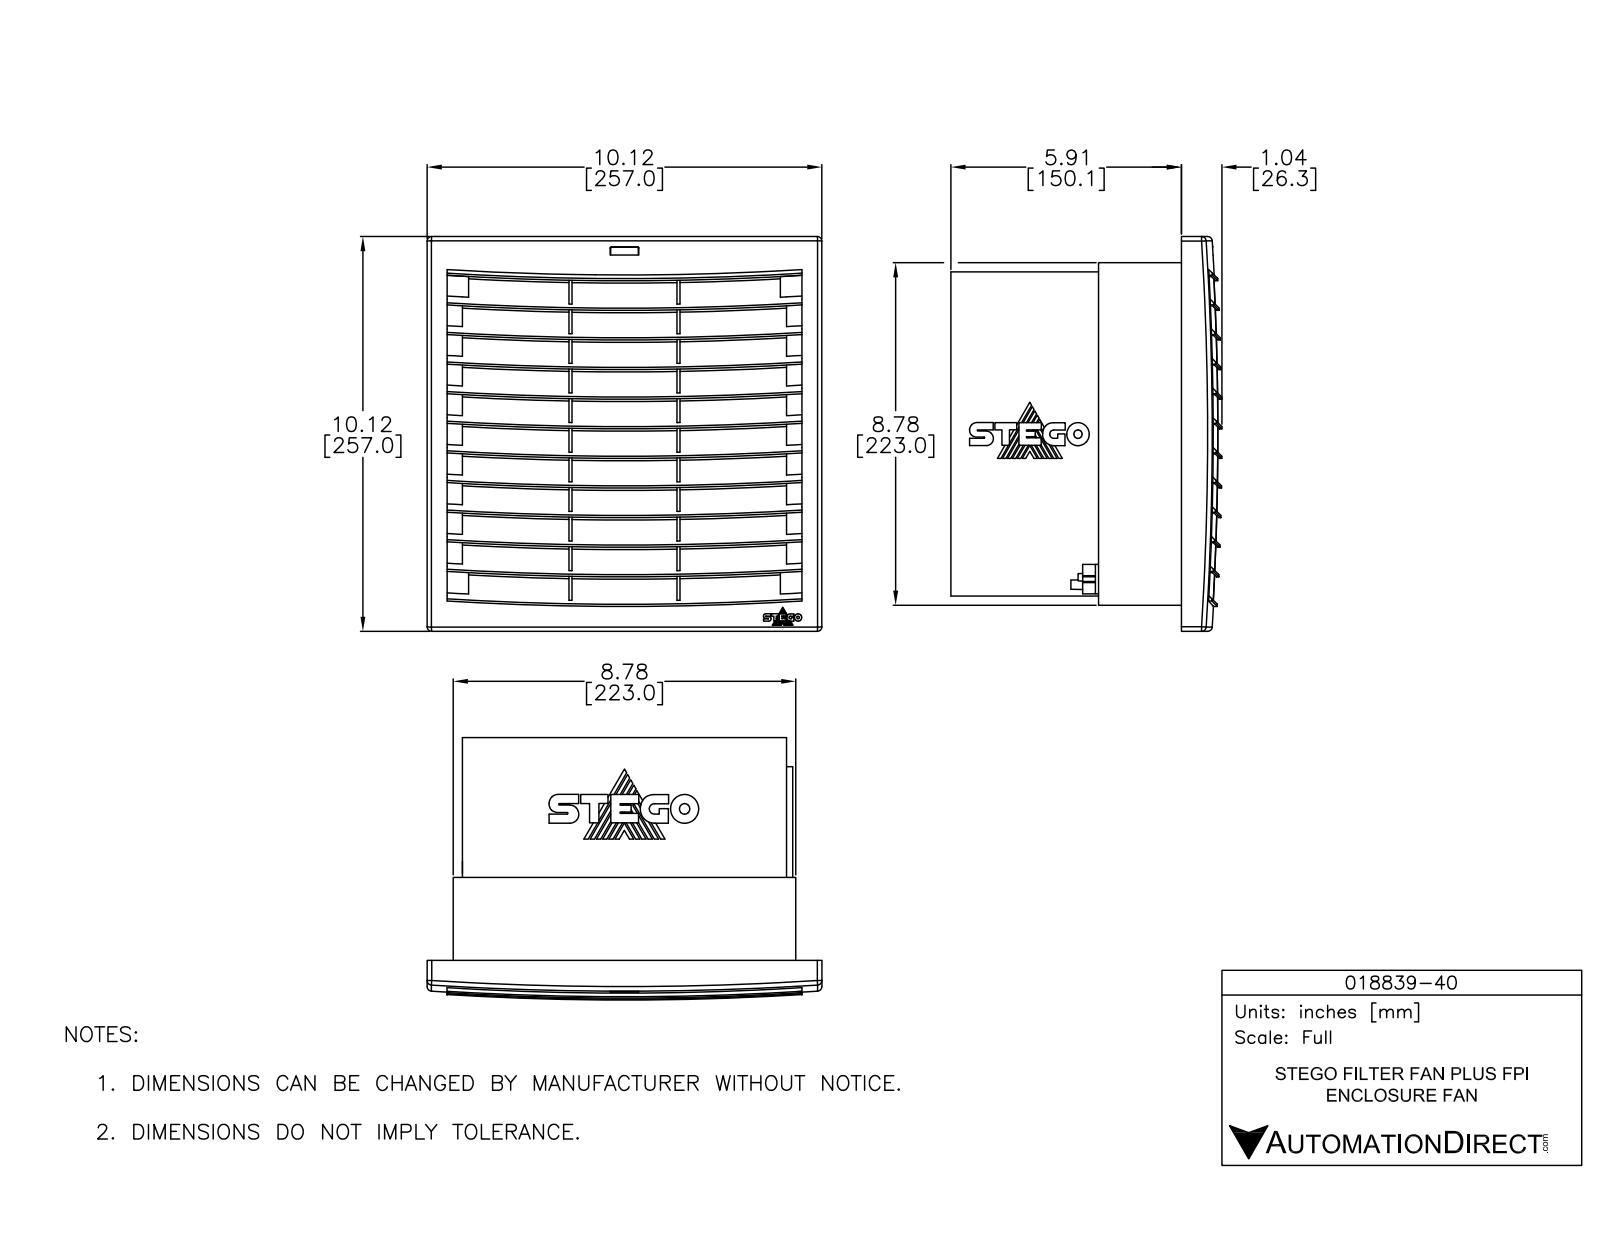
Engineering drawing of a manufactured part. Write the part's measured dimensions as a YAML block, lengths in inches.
part_name: "018839-40"
step_written_by: "SolidWorks 2018 (AUTOMOTIVE_DESIGN)"
units: inches
bodies: {solids: 1, faces: 808, planar: 462, cylindrical: 346, other: 0}
overall_size: [10.118, 10.118, 6.811]
volume: 155
surface_area: 918.5
round_holes:
  - {diameter: 2.268, count: 1}
  - {diameter: 3.018, count: 1}
  - {diameter: 3.769, count: 1}
  - {diameter: 4.487, count: 1}
  - {diameter: 4.52, count: 1}
  - {diameter: 5.27, count: 1}
  - {diameter: 5.42, count: 1}
  - {diameter: 6.021, count: 1}
  - {diameter: 6.353, count: 1}
  - {diameter: 6.929, count: 1}
  - {diameter: 7.463, count: 1}
round_bosses_or_shafts:
  - {diameter: 8.64, count: 1}
  - {diameter: 8.228, count: 1}
  - {diameter: 8.146, count: 1}
  - {diameter: 6.707, count: 1}
  - {diameter: 6.336, count: 1}
  - {diameter: 5.774, count: 1}
  - {diameter: 5.585, count: 1}
  - {diameter: 4.841, count: 1}
partial_cylinders:
  - {radius: 42.577, count: 21}
  - {radius: 3.361, count: 5}
  - {radius: 0.197, count: 4}
  - {radius: 0.26, count: 4}
  - {radius: 0.933, count: 1}
  - {radius: 1.311, count: 1}
  - {radius: 1.488, count: 1}
  - {radius: 1.777, count: 1}
face_to_face_distances: [0.536, 0.059, 2.145, 2.681, 1.609, 0.22, 8.56, 1.073, 1.072, 0.477]
